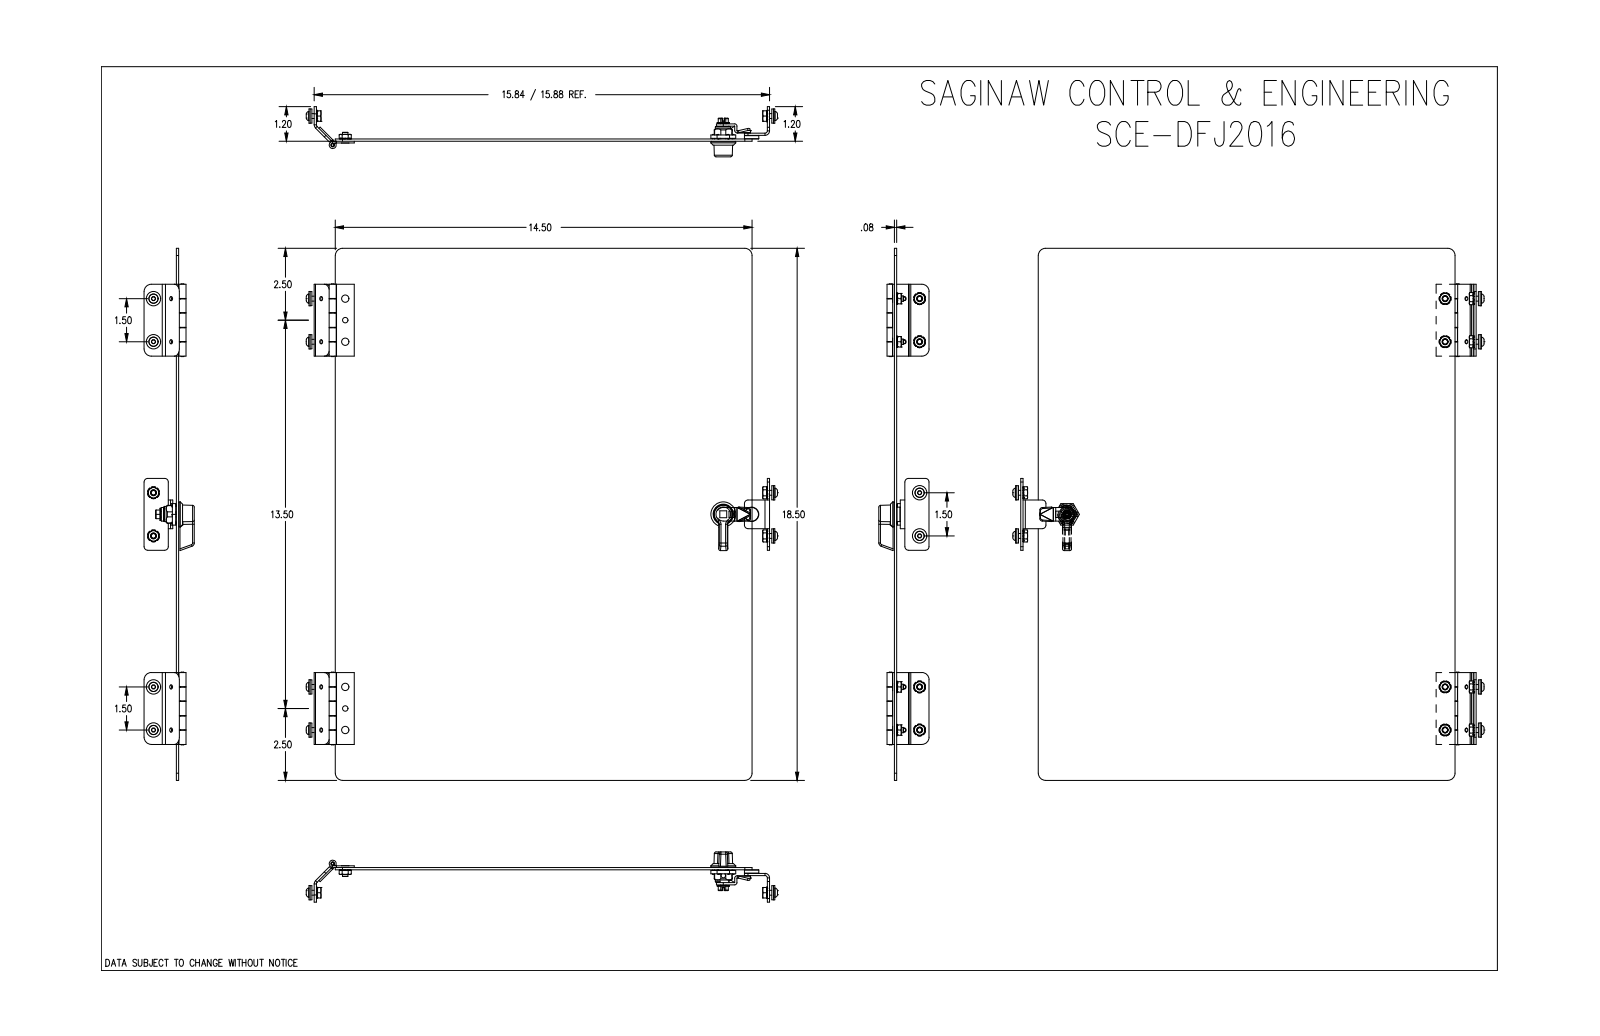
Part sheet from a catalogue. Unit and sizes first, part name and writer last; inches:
Units: inches
Overall size (bounding box): 18.5 × 16.396 × 1.746
Round holes (diameter × count): ⌀0.19 ×10, ⌀0.25 ×10, ⌀0.249 ×6, ⌀0.136 ×4, ⌀0.142 ×4, ⌀0.193 ×4, ⌀0.157 ×3, ⌀0.188 ×2, ⌀0.071 ×1, ⌀0.125 ×1, ⌀0.144 ×1, ⌀0.236 ×1
Round bosses / shafts (diameter × count): ⌀0.5 ×7, ⌀0.49 ×6, ⌀0.17 ×6, ⌀0.256 ×4, ⌀0.188 ×4, ⌀0.866 ×1, ⌀0.827 ×1, ⌀0.551 ×1
Partial cylindrical surfaces — rounded edges, fillets, slot ends (radius × count): R0.012 ×30, R0.125 ×18, R0.25 ×12, R0.02 ×10, R0.039 ×8, R0.004 ×4, R0.059 ×4, R0.083 ×4
Main face-to-face distances: 0.078, 0.06, 0.138, 15.766, 15.844, 15.688, 0.203, 0.735, 15.235, 0.657
Hole centre spacings: 1.5, 13.5, 0.75, 6.75, 12, 15, 0.949, 0.957
Volume: 23.06 in³ · Surface area: 609.2 in²
Bodies: 47 solids, 1574 faces (1048 planar, 290 cylindrical, 236 other)
Part name (STEP PRODUCT): SCE-DFJ2016
STEP written by: SolidWorks 2021 (AUTOMOTIVE_DESIGN)
